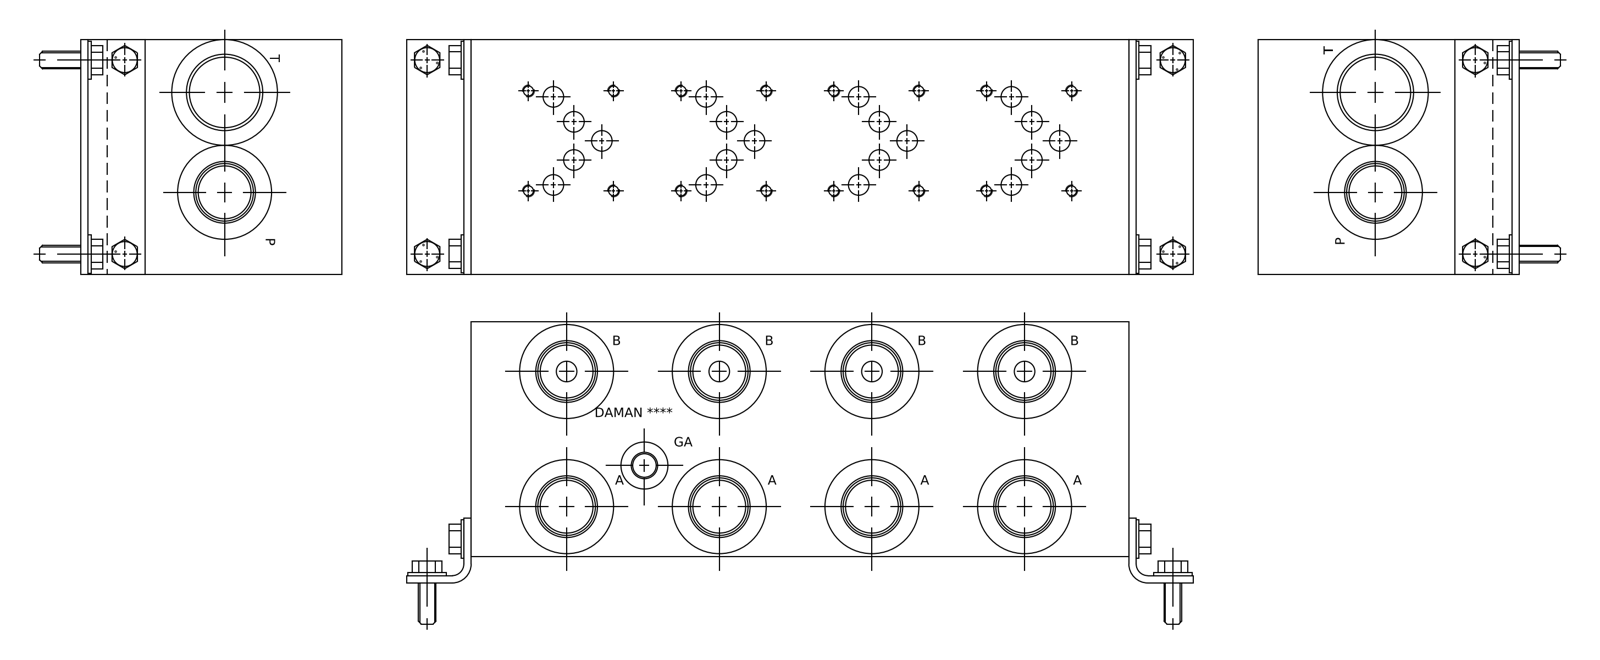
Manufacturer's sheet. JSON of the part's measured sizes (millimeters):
{"part_name": "Part_AD05JP043S_3D", "step_written_by": "Autodesk Inventor 2020 (AUTOMOTIVE_DESIGN)", "units": "millimeters", "bodies": {"solids": 1, "faces": 865, "planar": 437, "cylindrical": 133, "other": 295}, "overall_size": [355.6, 127, 127], "volume_mm3": 5305000, "surface_area_mm2": 273172, "round_holes": [[5.11, 16], [6.35, 16], [31.27, 9], [33.76, 9], [49.12, 9], [10.31, 8], [11.13, 8], [28.57, 8], [33.35, 8], [35.51, 8], [9.53, 6], [7.92, 2]], "face_to_face_distances": [127, 0.79, 355.6, 126.21, 354.81, 354.02, 19.05, 19.84, 107.16, 335.76], "hole_center_spacings": [82.55, 165.1, 18.27, 68.25, 110.22, 247.65, 13.88, 94.65]}
